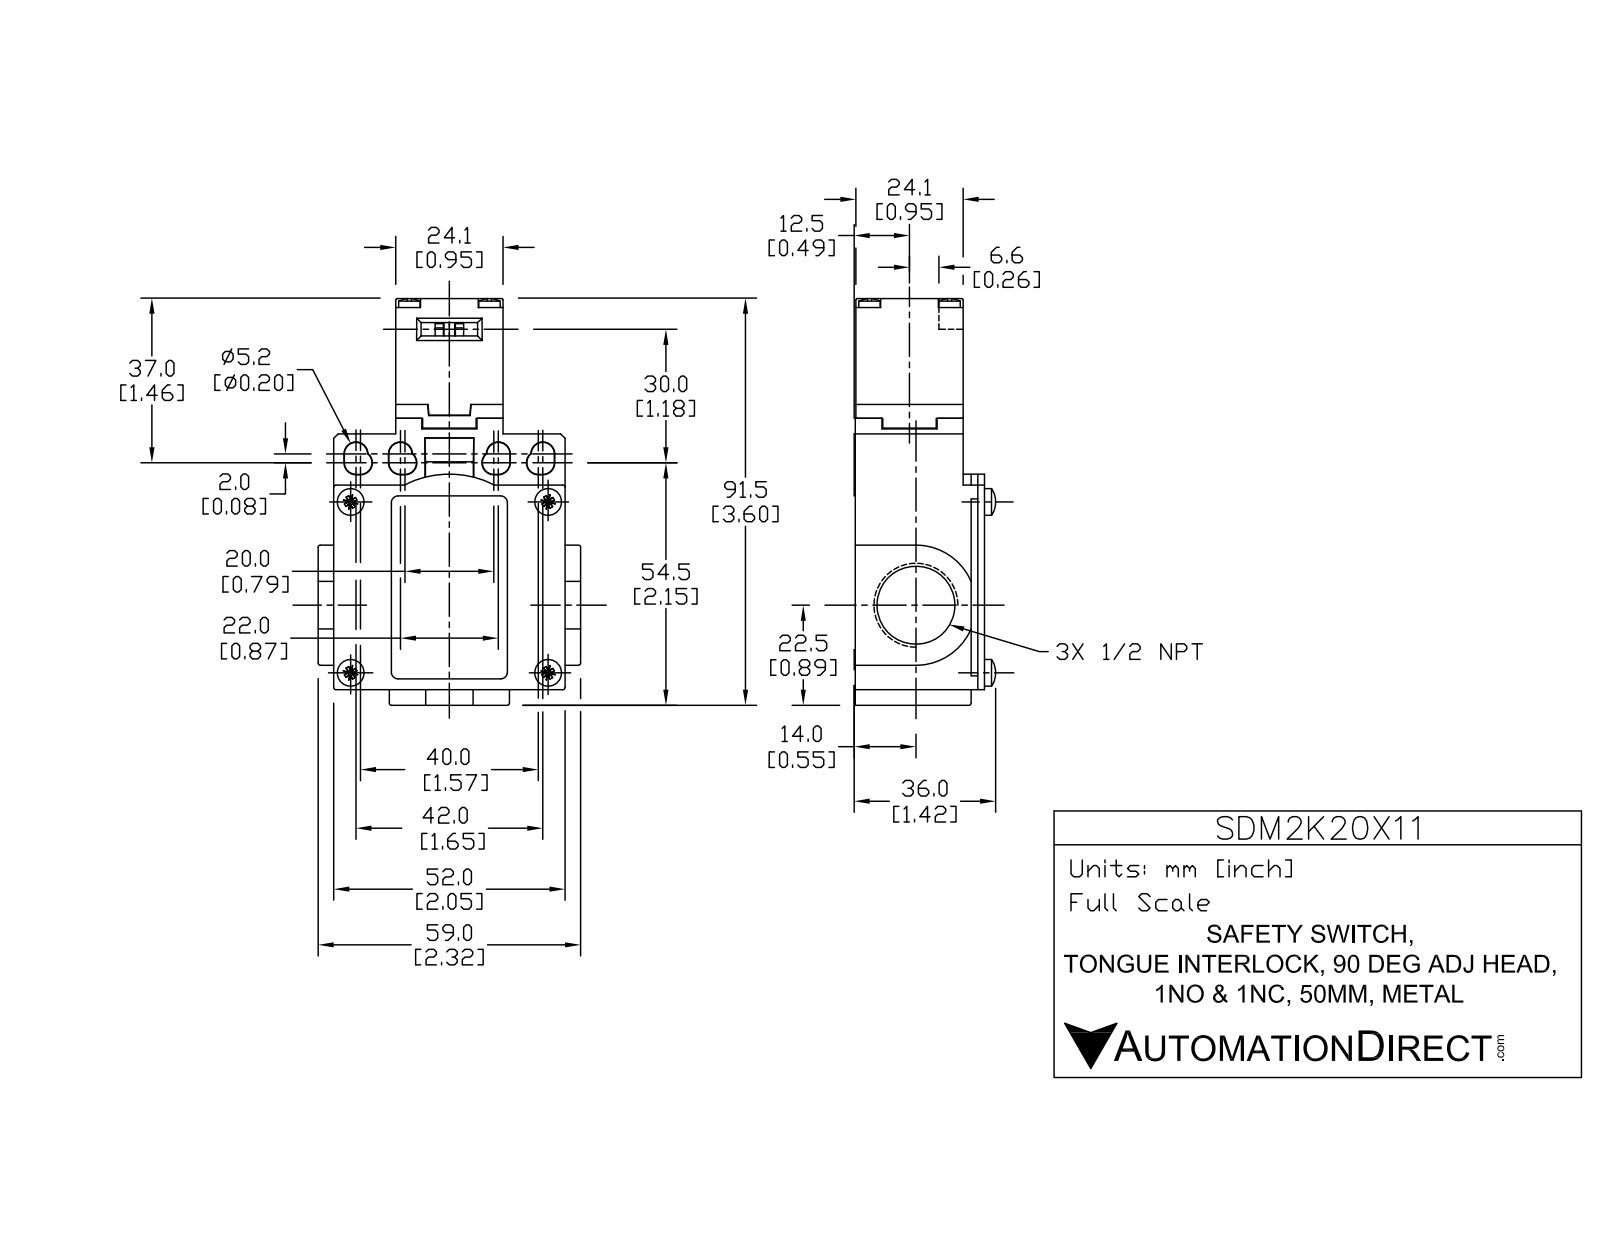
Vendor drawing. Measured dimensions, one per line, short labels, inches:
name: SDM2K20X11
written by: SolidWorks 2017 (AUTOMOTIVE_DESIGN)
unit: in
bodies: 2 solids, 198 faces (105 planar, 73 cylindrical, 20 other)
size: 3.594 × 2.323 × 1.252
volume: 6.047 in³; area: 33.47 in²
holes: 2× ⌀0.669, 2× ⌀0.748
bosses: 4× ⌀0.217, 4× ⌀0.189
rounds: 12× R0.102, 10× R0.02, 4× R0.012, 4× R0.098, 2× R0.531, 1× R0.394, 1× R0.4, 1× R0.866
face distances: 1.144, 0.945, 0.551, 1.496, 0.138, 0.199, 2.047, 2.307, 0.236, 2.185
